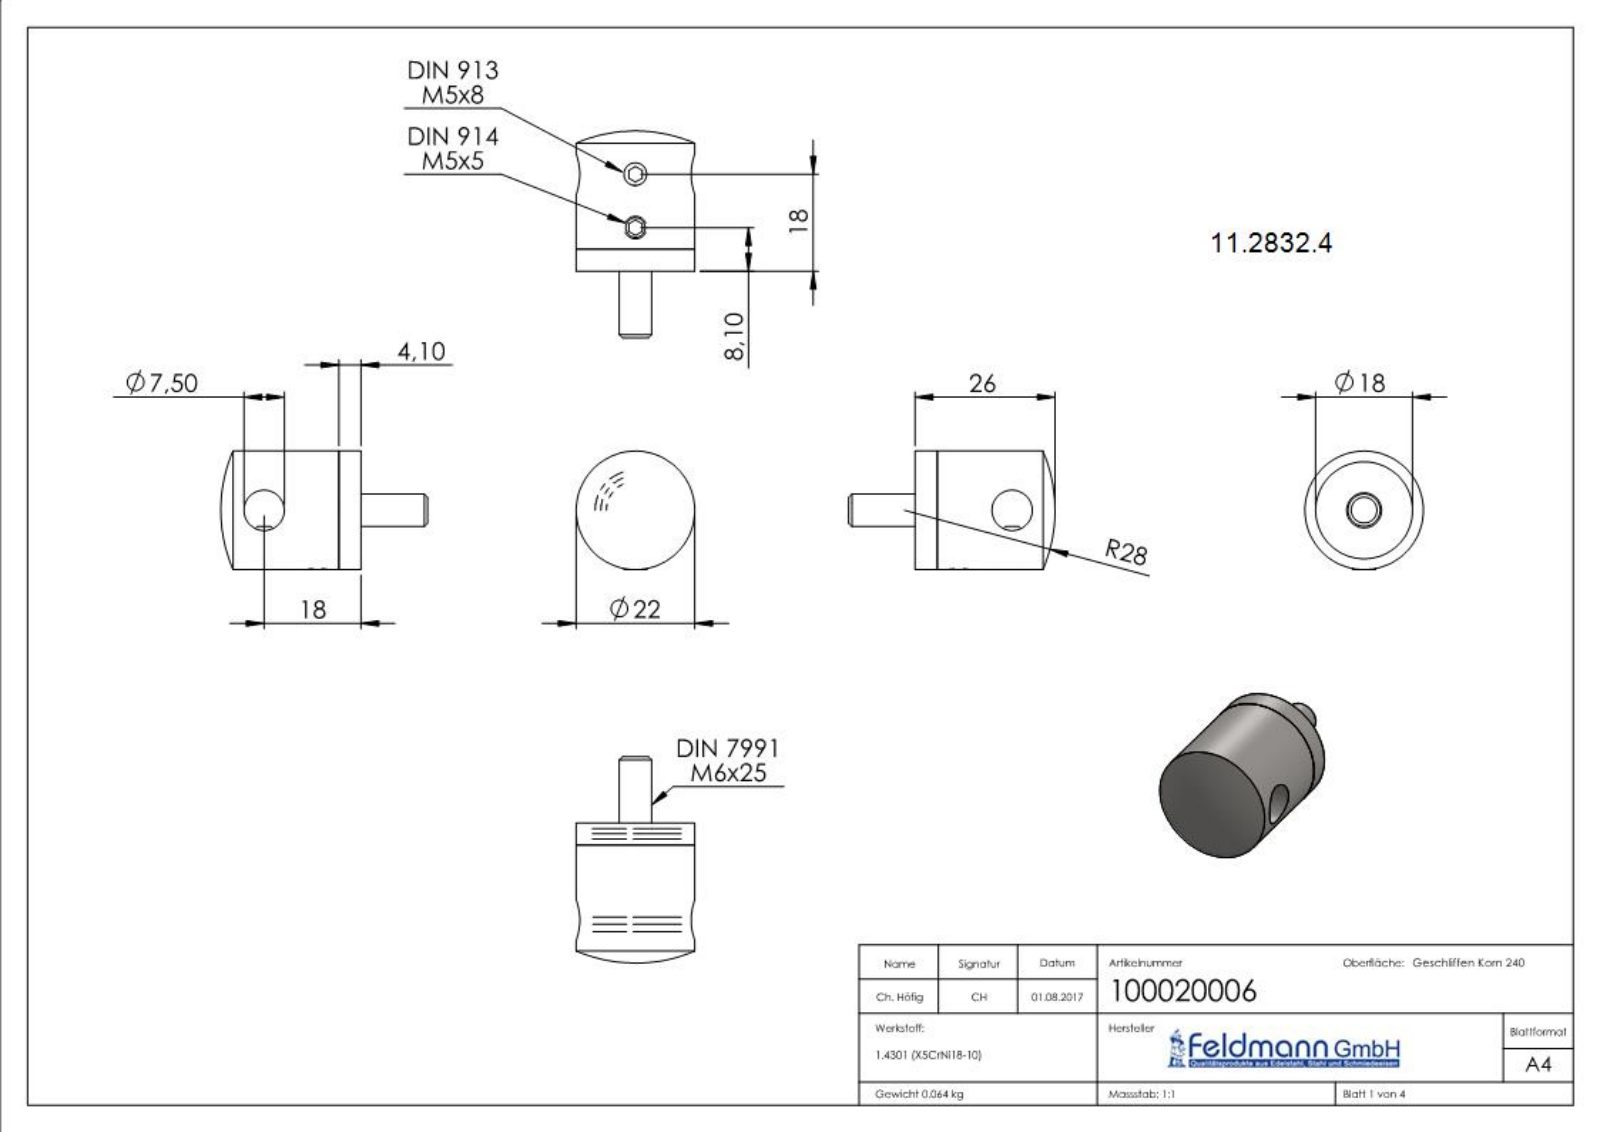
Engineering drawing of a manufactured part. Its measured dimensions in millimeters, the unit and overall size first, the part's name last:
Units: millimetres
Overall size (bounding box): 82 × 33.5 × 22
Round holes (diameter × count): ⌀4.2 ×2, ⌀6.5 ×1, ⌀10.2 ×1, ⌀12.1 ×1, ⌀18 ×1
Round bosses / shafts (diameter × count): ⌀5 ×2, ⌀22 ×1, ⌀12 ×1, ⌀6 ×1
Partial cylindrical surfaces — rounded edges, fillets, slot ends (radius × count): R21.2 ×1
Main face-to-face distances: 9.6, 7.6, 2, 25.65, 18.05, 16.05, 2.5, 4, 0.65, 6.95
Hole centre spacings: 12.4
Volume: 8 994 mm³ · Surface area: 6 081 mm²
Bodies: 5 solids, 74 faces (35 planar, 15 cylindrical, 24 other)
Part name (STEP PRODUCT): 100020006; 10002X00X Teil1_50399-240A Teil1; DIN 914 M5x5; 10002X00X Teil2_10002400X Teil2 Keyshot (+7 more)
STEP written by: SolidWorks 2018 (CONFIG_CONTROL_DESIGN)
